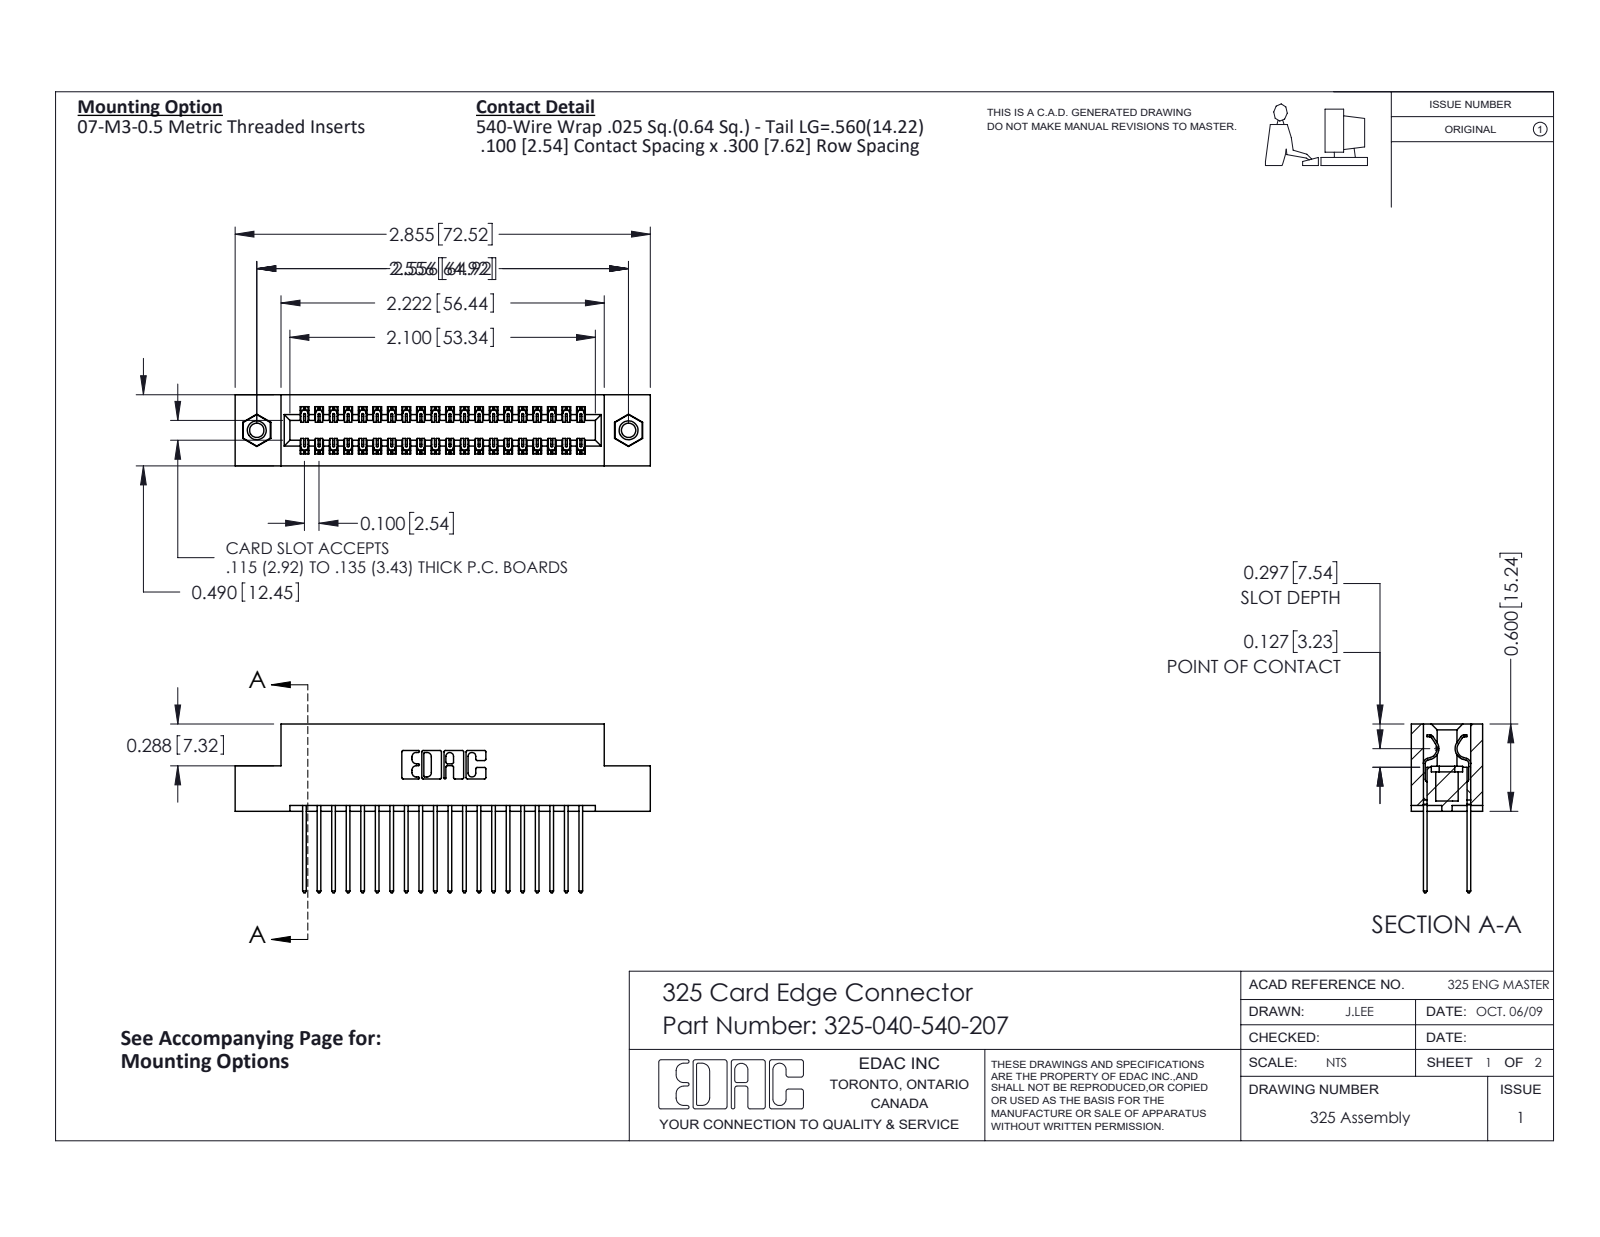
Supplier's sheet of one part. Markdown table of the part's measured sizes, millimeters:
| quantity | value |
| --- | --- |
| part name | 325 Part_TI; 345-250-001_345-250-005-103; 325-292-001_325-293-140; 325-040-540-207 |
| STEP written by | SolidWorks 2016 (CONFIG_CONTROL_DESIGN) |
| units | millimeters |
| bodies | 43 solids, 2254 faces (1542 planar, 696 cylindrical, 16 other) |
| overall size | 72.5 × 29.5 × 12.4 |
| volume | 9 310 mm³ |
| surface area | 11 480 mm² |
| round holes (diameter × count) | 2.5 × 2, 3.2 × 2, 4.1 × 2 |
| round bosses / shafts (diameter × count) | 3.9 × 2 |
| partial cylindrical surfaces (radius × count) | 0.2 × 60, 0.3 × 40, 0.3 × 22, 0.2 × 6, 0.8 × 6, 0.7 × 3, 0.4 × 2, 0.6 × 2 |
| main face-to-face distances | 2.1, 10.3, 7.6, 2.7, 9.7, 0.6, 12.4, 8.3, 1, 7 |
| hole center spacings | 64.9 |
